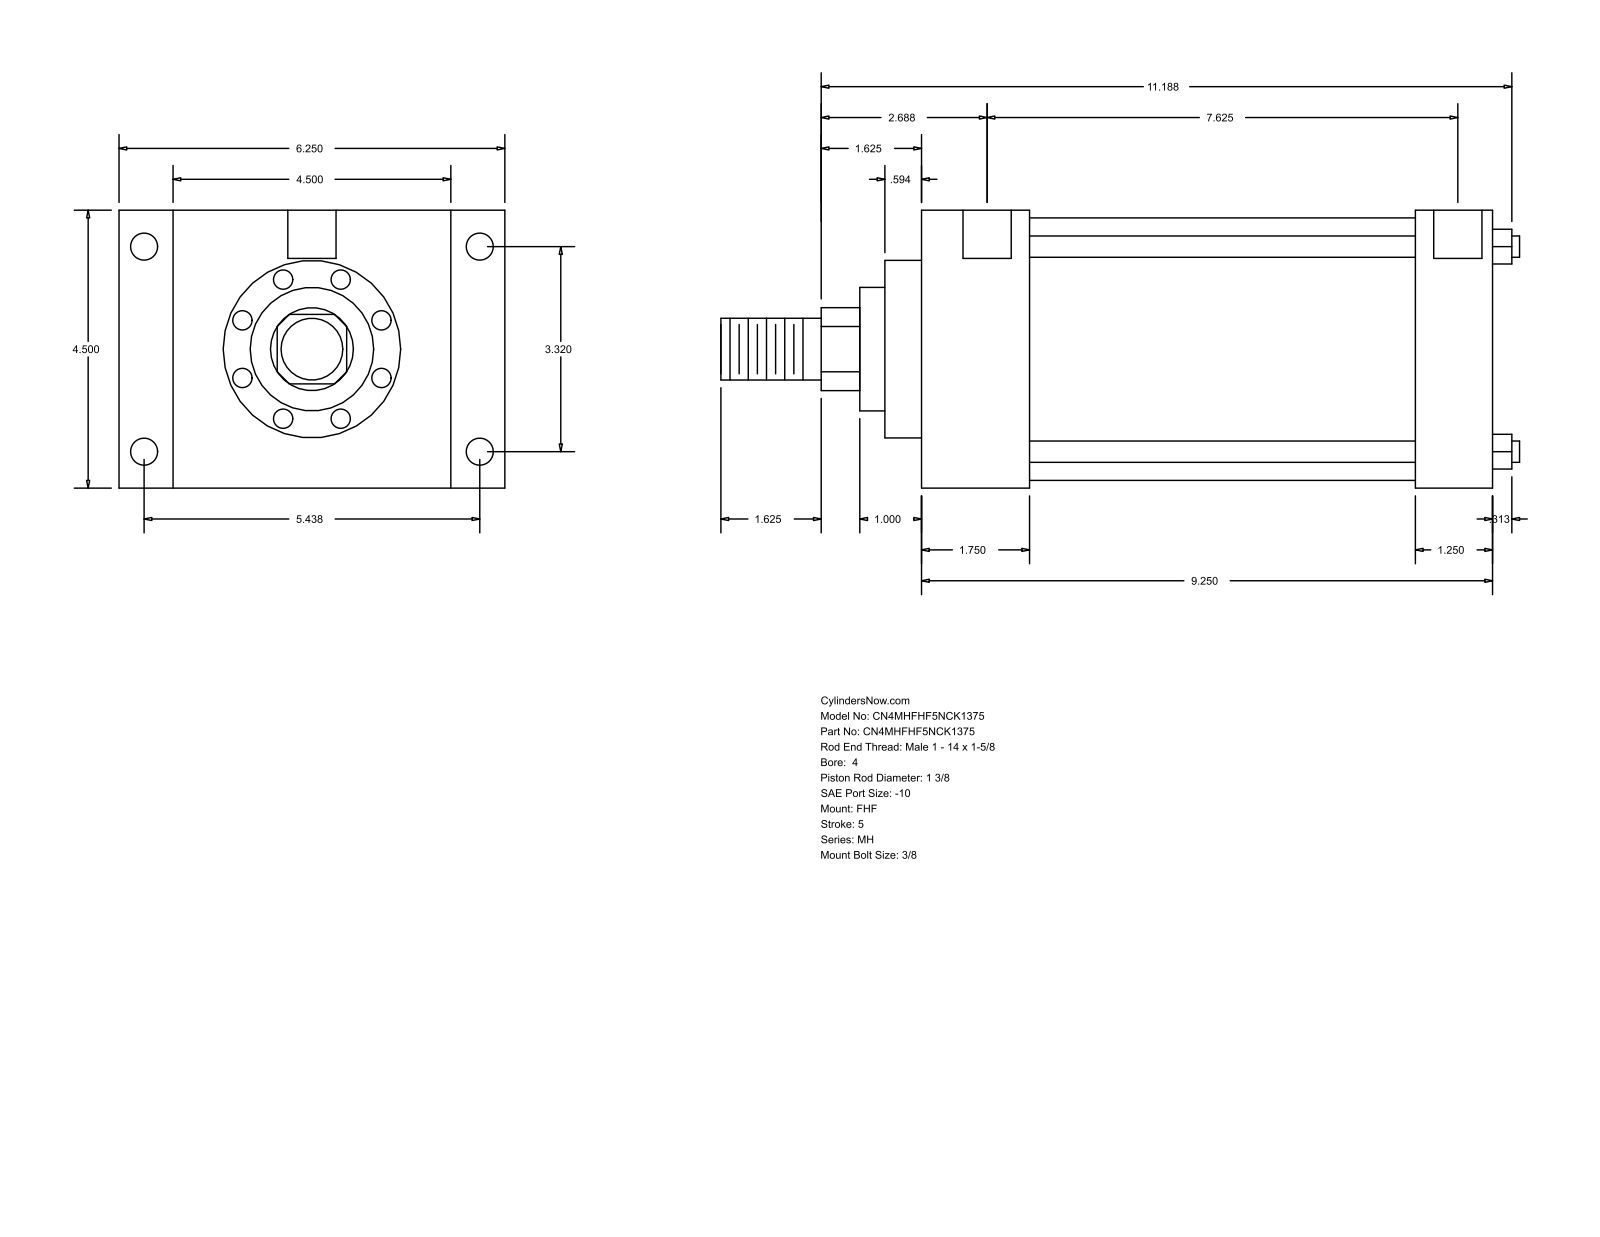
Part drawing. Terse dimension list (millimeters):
name: MH_FHF__0400_1.375
written by: GSSL Pune (CONFIG_CONTROL_DESIGN)
unit: mm
bodies: 0 solids, 90 faces (61 planar, 29 cylindrical, 0 other)
size: 328.61 × 158.75 × 114.3
holes: 4× ⌀8.73, 4× ⌀11.13, 2× ⌀19.84
bosses: 4× ⌀8.76, 1× ⌀107.95, 1× ⌀73.03, 1× ⌀50.8, 1× ⌀34.92, 1× ⌀25.4
rounds: 1× R17.06
face distances: 114.3, 234.96, 44.45, 190.51, 22.23, 136.53, 158.76, 158.75, 203.2, 31.76
hole spacings: 84.32, 138.12, 161.82, 196.85, 1.58, 1.59, 193.68, 195.26
